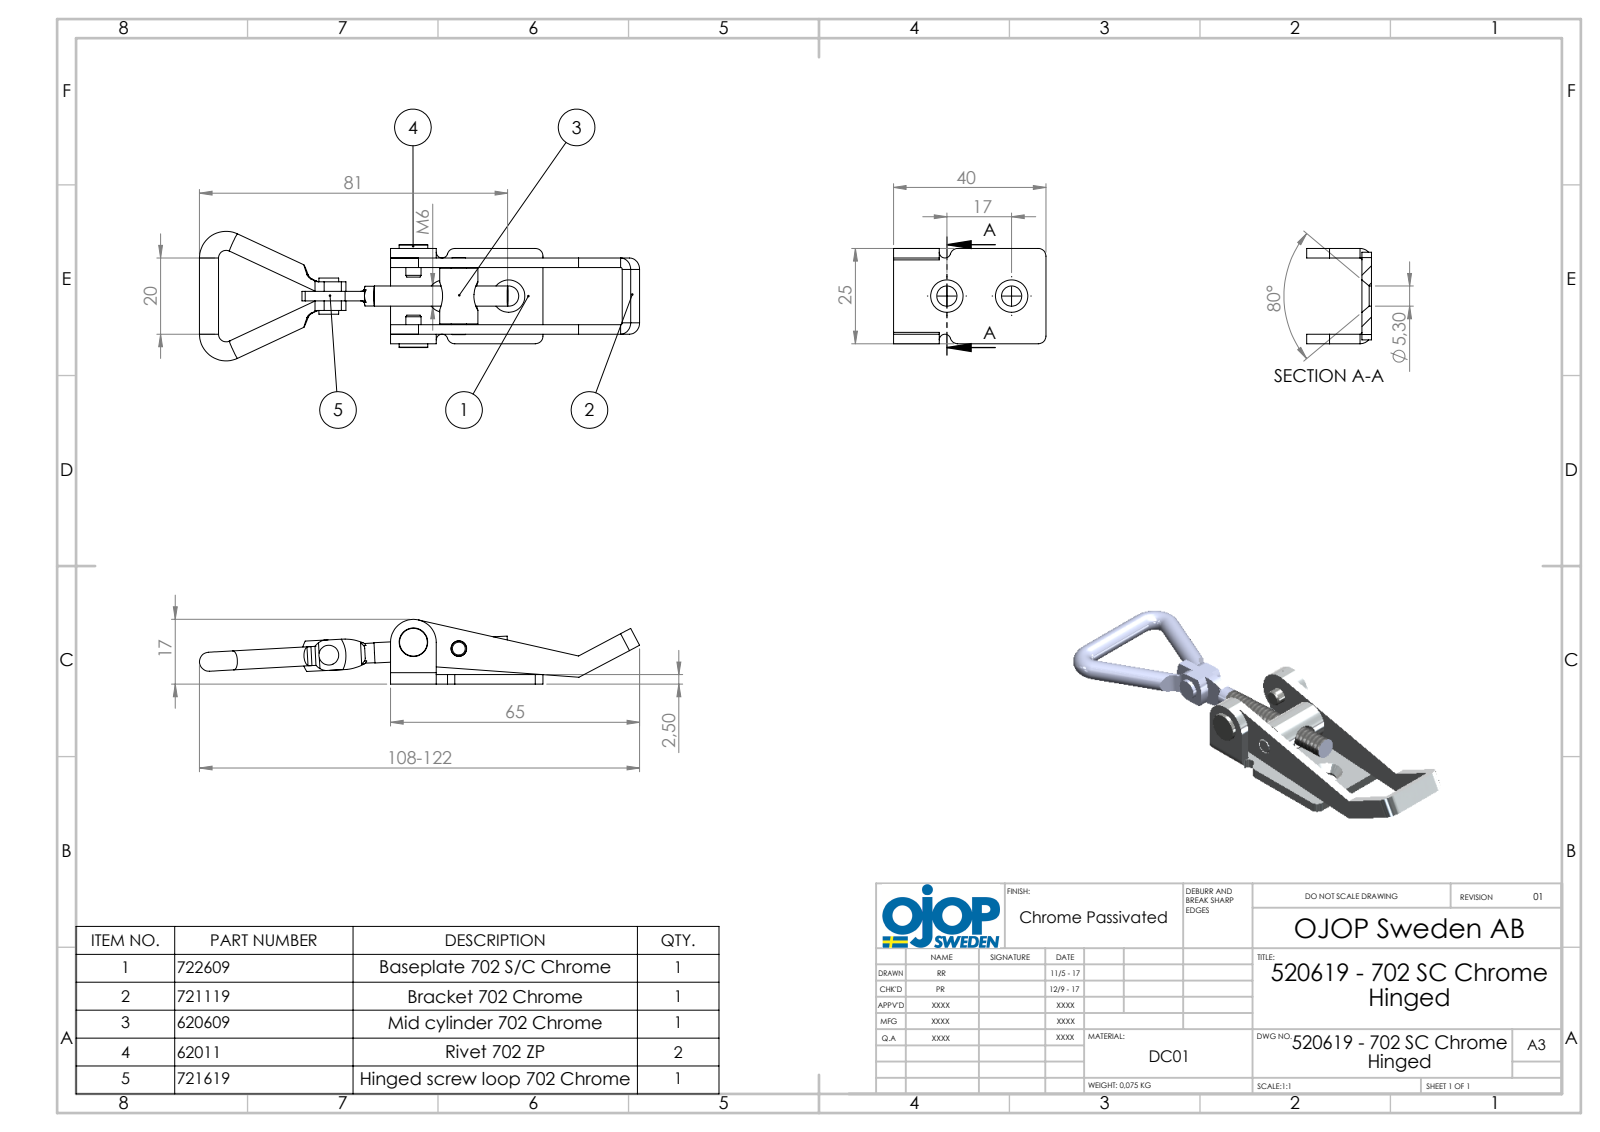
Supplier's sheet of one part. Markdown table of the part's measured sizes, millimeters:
| quantity | value |
| --- | --- |
| part name | 702 - Rulle; 702 - Ansatsnit; 702 - Bygel; 702 - Skruv till ledad M6 (+5 more) |
| STEP written by | SolidWorks 2015 (AUTOMOTIVE_DESIGN) |
| units | millimeters |
| bodies | 8 solids, 207 faces (80 planar, 101 cylindrical, 26 other) |
| overall size | 115.53 × 34 × 17 |
| volume | 10 043 mm³ |
| surface area | 10 133 mm² |
| round holes (diameter × count) | 4.1 × 3, 5.3 × 2, 5 × 1, 6 × 1 |
| round bosses / shafts (diameter × count) | 5 × 3, 4 × 2, 10 × 1, 7.5 × 1, 5.3 × 1, 5.2 × 1, 5.18 × 1 |
| partial cylindrical surfaces (radius × count) | 2 × 8, 1 × 6, 0.5 × 4, 3 × 4, 1.5 × 2, 6.78 × 2, 12.31 × 2, 3.85 × 1 |
| main face-to-face distances | 2.5, 20, 17.5, 8.75, 11.25, 5, 15, 6.25, 13.75, 22.5 |
| hole center spacings | 12.03, 17, 22.47, 34.16 |
